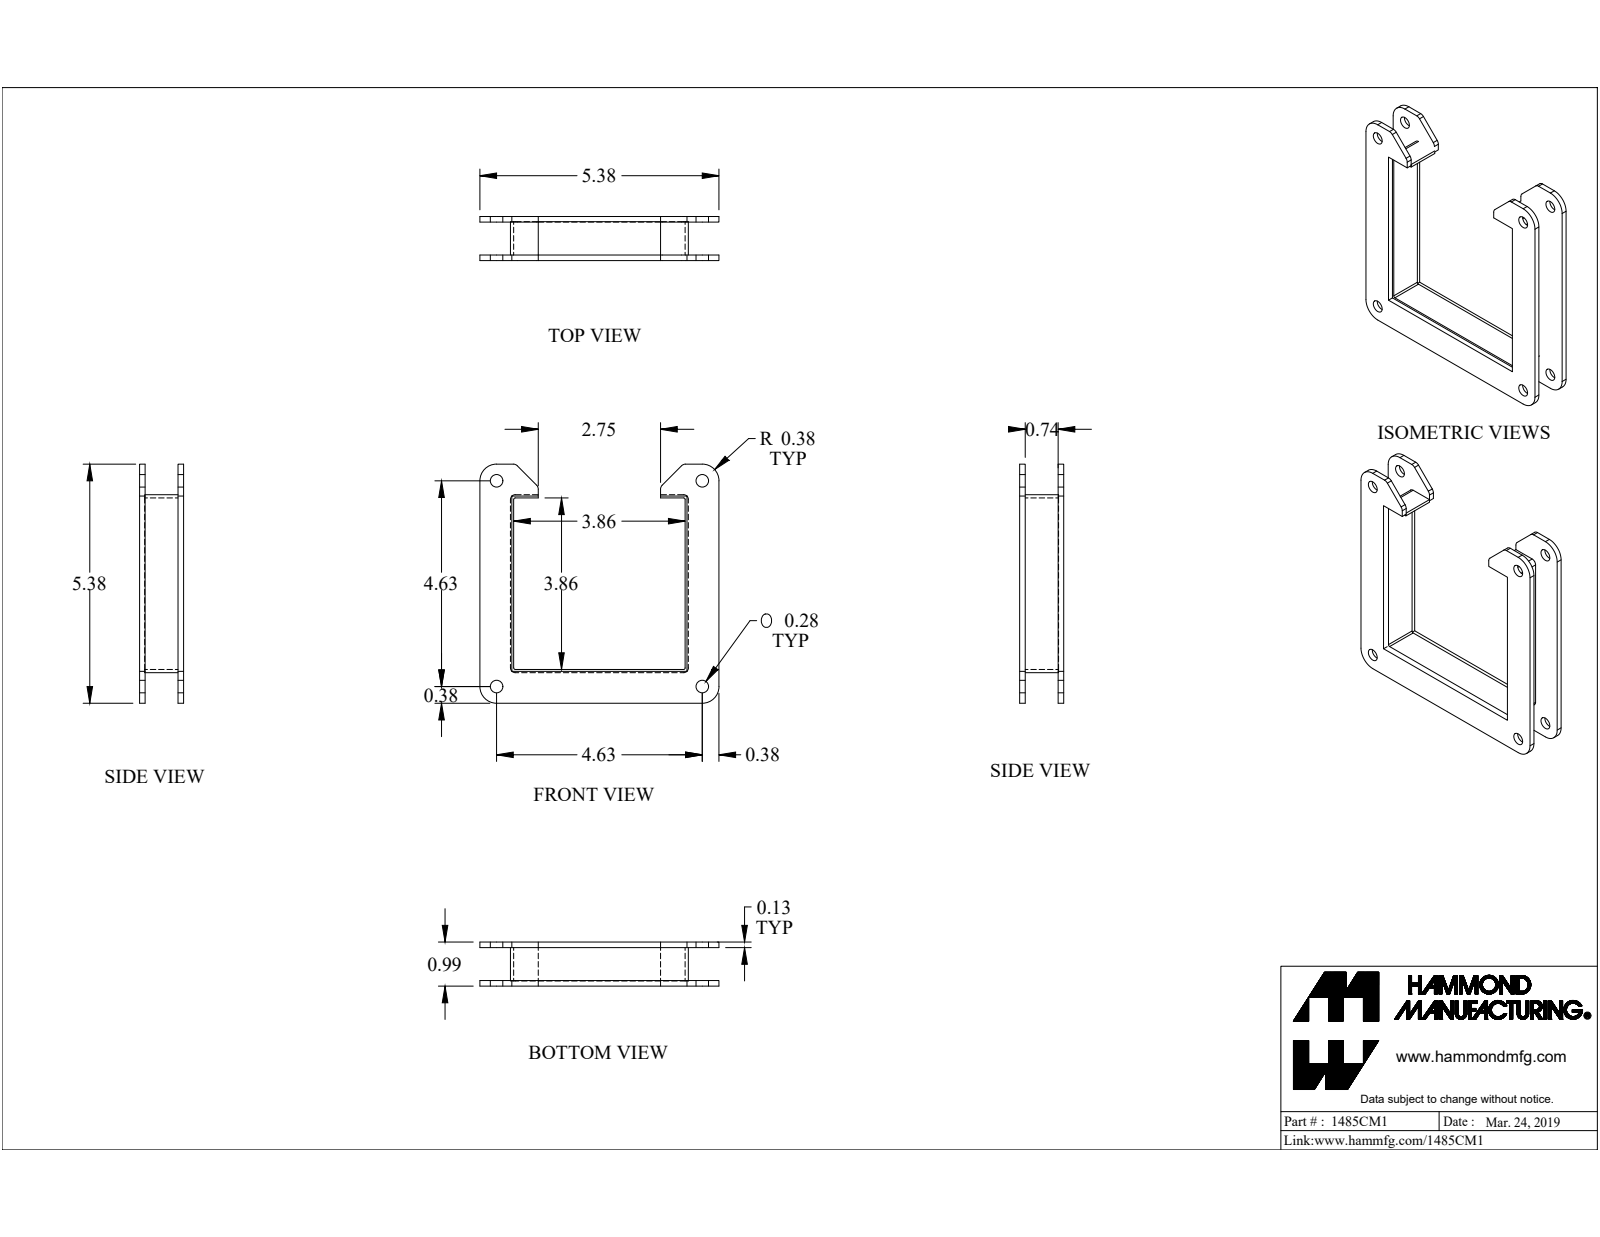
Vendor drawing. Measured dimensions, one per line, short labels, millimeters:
name: 1485CM1
written by: SolidWorks 2019 (CONFIG_CONTROL_DESIGN)
unit: mm
bodies: 3 solids, 78 faces (46 planar, 32 cylindrical, 0 other)
size: 136.5 × 136.5 × 25.1
volume: 55 490 mm³; area: 47 200 mm²
holes: 4× ⌀7.1
rounds: 4× R0.9, 4× R2.7, 4× R3.2, 4× R9.5
face distances: 22, 3.2, 25.1, 18.8, 1.8, 99.8, 17.4, 19.3, 101.6, 97.9
hole spacings: 117.5, 166.1
